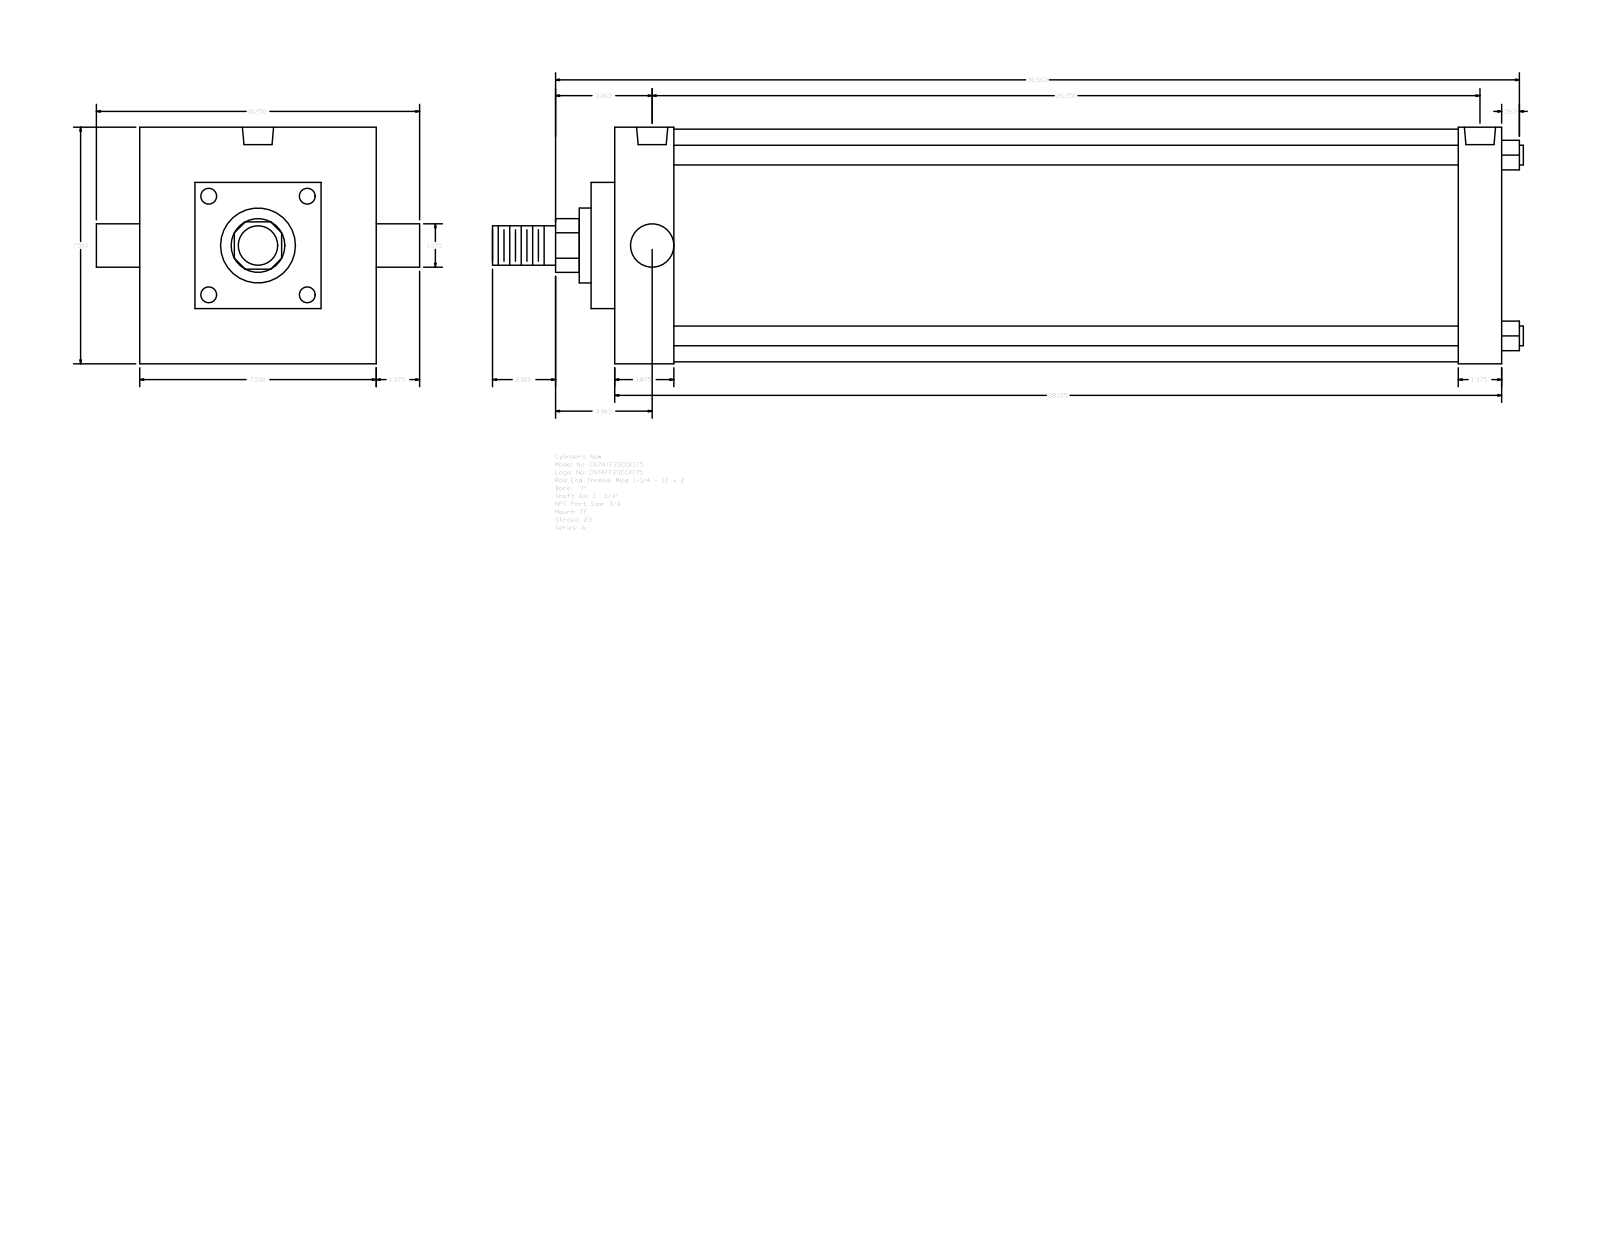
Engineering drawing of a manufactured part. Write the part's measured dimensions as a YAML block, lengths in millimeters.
part_name: "A_TF__0700_1.75"
step_written_by: "GSSL Pune (CONFIG_CONTROL_DESIGN)"
units: millimeters
bodies: {solids: 0, faces: 89, planar: 65, cylindrical: 24, other: 0}
overall_size: [830.26, 260.35, 190.5]
round_holes:
  - {diameter: 15.08, count: 3}
  - {diameter: 25.12, count: 2}
round_bosses_or_shafts:
  - {diameter: 15.88, count: 4}
  - {diameter: 187.32, count: 1}
  - {diameter: 60.33, count: 1}
  - {diameter: 44.45, count: 1}
  - {diameter: 34.92, count: 1}
  - {diameter: 31.75, count: 1}
partial_cylinders:
  - {radius: 21.63, count: 1}
face_to_face_distances: [190.5, 714.38, 146.05, 19.05, 47.63, 666.75, 679.46, 631.83, 34.92, 44.45]
hole_center_spacings: [5.56, 661.19, 655.63, 666.75]
